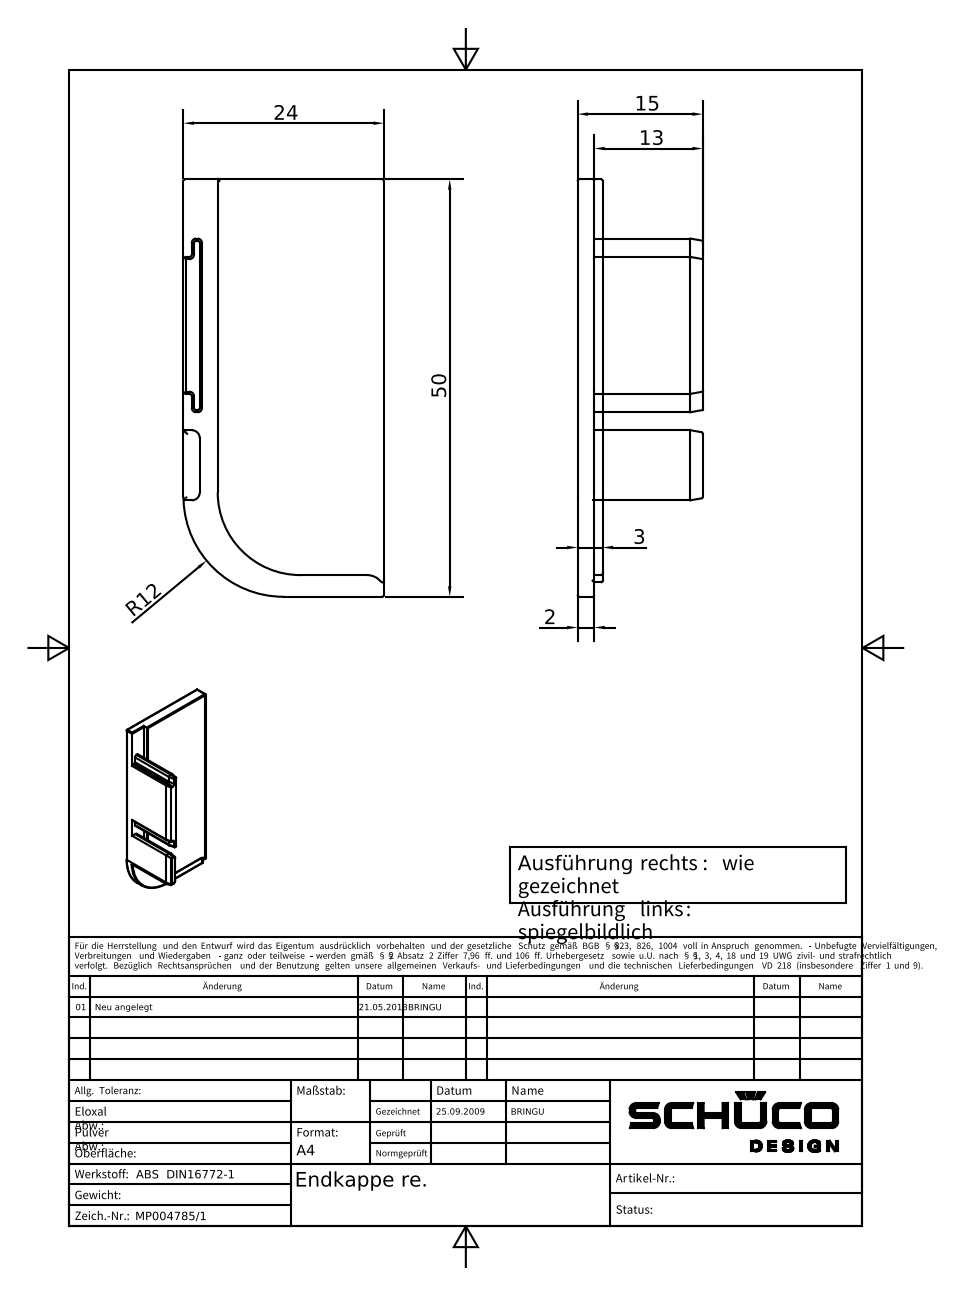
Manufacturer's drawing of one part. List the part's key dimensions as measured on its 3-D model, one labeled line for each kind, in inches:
Part name (STEP PRODUCT): MP004785
STEP written by: Autodesk Inventor 2024 (AUTOMOTIVE_DESIGN)
Units: inches
Bodies: 1 solid, 89 faces (33 planar, 32 cylindrical, 24 other)
Overall size (bounding box): 1.969 × 0.945 × 0.591
Volume: 0.243 in³ · Surface area: 5.499 in²
Partial cylindrical surfaces — rounded edges, fillets, slot ends (radius × count): R0.008 ×19, R0.012 ×4, R0.02 ×4, R0.037 ×2, R0.083 ×1, R0.39 ×1, R0.472 ×1
Main face-to-face distances: 0.118, 0.087, 0.039, 0.079, 0.945, 0.858, 0.077, 0.868, 0.591, 0.512
